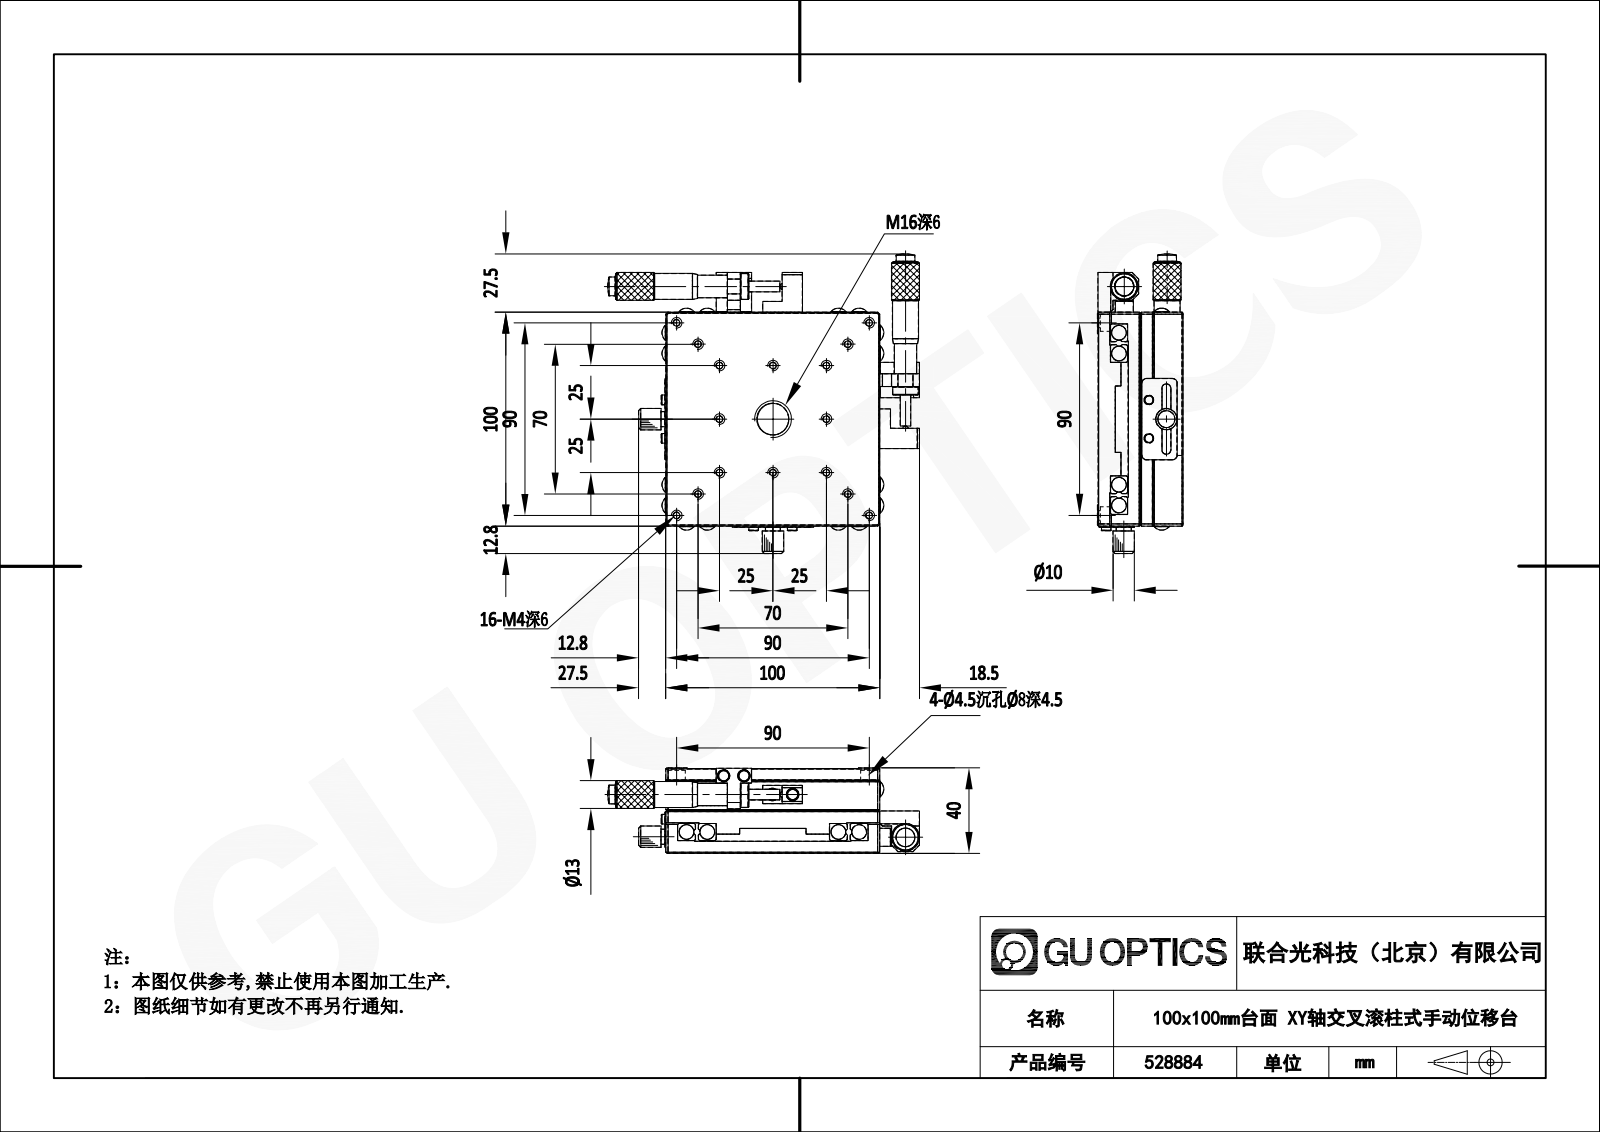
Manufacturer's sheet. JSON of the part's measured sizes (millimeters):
{"part_name": "528884", "step_written_by": "SolidWorks 2020 (CONFIG_CONTROL_DESIGN)", "units": "millimeters", "bodies": {"solids": 8, "faces": 5030, "planar": 534, "cylindrical": 1216, "other": 3280}, "overall_size": [143.99, 135.28, 41.08], "volume_mm3": 363889, "surface_area_mm2": 140824, "round_holes": [[2.55, 48], [4.44, 48], [3.2, 32], [2.46, 30], [6, 28], [3.24, 16], [2.46, 14], [1.57, 12], [1.57, 12], [3.1, 4], [4.5, 4], [5.8, 4]], "round_bosses_or_shafts": [[5, 8], [4, 8], [3.94, 8], [2.5, 8], [11.28, 2], [6.5, 2], [6, 2], [3, 2]], "partial_cylinders_radius": [[1.7, 4], [2, 4], [2.19, 4], [4.98, 2]], "face_to_face_distances": [20, 6, 7.5, 14, 0.5, 12.5, 6.5, 8, 19.8, 12.3], "hole_center_spacings": [15, 16.55, 75.5, 30, 30.81, 79.85, 7, 45]}
